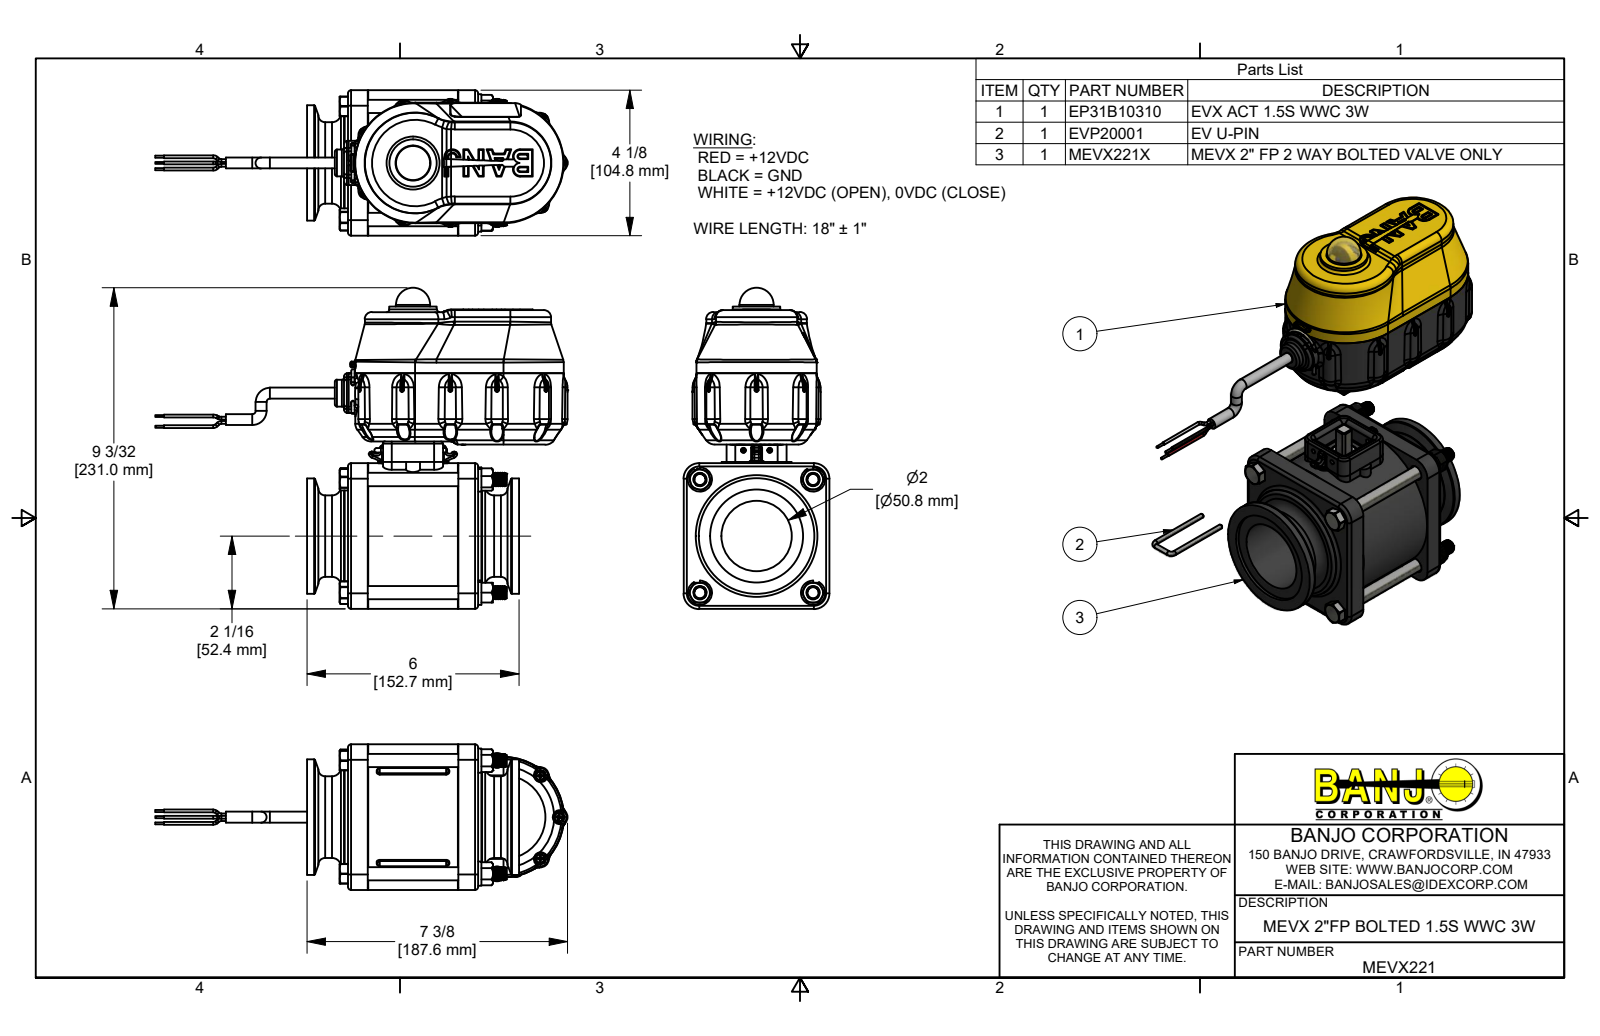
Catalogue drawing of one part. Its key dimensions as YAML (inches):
part_name: "MEVX221; MEVX221X; MEVX25254A; MEVX25254AX (+8 more)"
step_written_by: "Autodesk Inventor 2019 (AUTOMOTIVE_DESIGN)"
units: inches
bodies: {solids: 96, faces: 11075, planar: 2792, cylindrical: 3341, other: 4942}
overall_size: [11.685, 9.095, 4.125]
volume: 71.28
surface_area: 751.6
round_holes:
  - {diameter: 0.095, count: 11}
  - {diameter: 0.15, count: 11}
  - {diameter: 0.08, count: 7}
  - {diameter: 0.107, count: 4}
  - {diameter: 0.126, count: 4}
  - {diameter: 0.136, count: 4}
  - {diameter: 0.148, count: 4}
  - {diameter: 0.15, count: 4}
  - {diameter: 0.17, count: 4}
  - {diameter: 0.307, count: 4}
  - {diameter: 0.385, count: 4}
  - {diameter: 0.438, count: 4}
round_bosses_or_shafts:
  - {diameter: 0.324, count: 60}
  - {diameter: 0.25, count: 17}
  - {diameter: 0.08, count: 15}
  - {diameter: 0.14, count: 11}
  - {diameter: 0.108, count: 11}
  - {diameter: 0.085, count: 11}
  - {diameter: 0.058, count: 6}
  - {diameter: 0.375, count: 5}
partial_cylinders:
  - {radius: 0.013, count: 180}
  - {radius: 0.04, count: 145}
  - {radius: 0.01, count: 92}
  - {radius: 0.02, count: 74}
  - {radius: 0.005, count: 53}
  - {radius: 0.03, count: 38}
  - {radius: 0.08, count: 28}
  - {radius: 0.06, count: 24}
face_to_face_distances: [0.1, 2.565, 0.06, 0.729, 0.645, 3.045, 2.485, 0.56, 3.13, 0.085]
hole_center_spacings: [2.265, 2.715, 3.204, 1.662, 1.774, 2.458, 2.69, 2.73]
